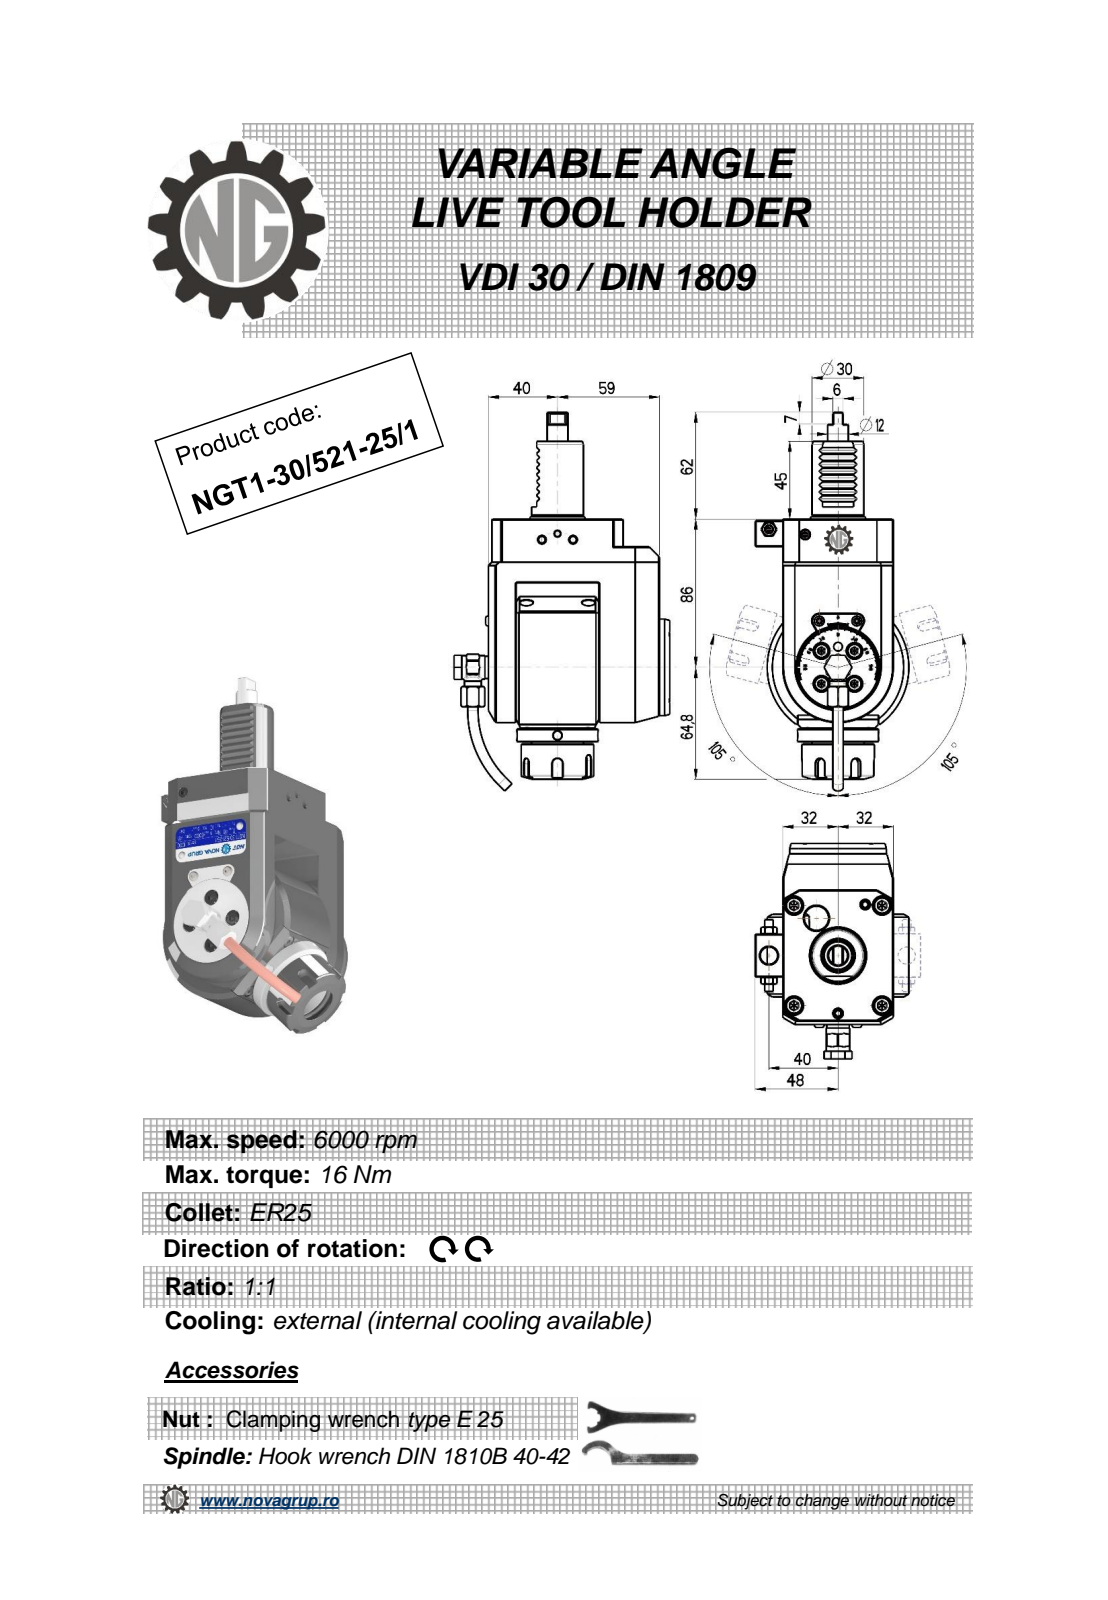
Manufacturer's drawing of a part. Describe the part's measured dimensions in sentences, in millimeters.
The part is named "NGT1_30_521_25_1". Its 3-D file was written by "PRO/ENGINEER BY PARAMETRIC TECHNOLOGY CORPORATION, 2010280 (CONFIG_CONTROL_DESIGN)". It is 1 solid with 544 faces: 229 planar, 132 cylindrical and 183 other. Overall it measures 219.67 by 124.9 by 89 millimeters. Its volume is 779 434 cubic millimeters and its surface area 74 506 square millimeters. Round holes: 3 of diameter 4, 2 of diameter 5, 2 of diameter 10, 1 of diameter 3, 1 of diameter 4.2, 1 of diameter 6.2, 1 of diameter 9, 1 of diameter 9.5, 1 of diameter 11, 1 of diameter 20.3. Round bosses or shafts: 2 of diameter 6, 2 of diameter 5.7, 1 of diameter 82, 1 of diameter 56, 1 of diameter 47, 1 of diameter 42, 1 of diameter 35, 1 of diameter 30. Partial cylindrical surfaces (rounded edges, fillets, slot ends): 12 of radius 0.26, 8 of radius 0.3, 6 of radius 0.16, 6 of radius 0.5, 5 of radius 3, 2 of radius 1, 1 of radius 7.7, 1 of radius 32. The main face-to-face distances are 64, 16, 37, 6, 99, 105, 21, 35, 14, 41. The hole center spacings are 0.4, 39.45, 40, 49, 49.4, 63.25, 63.56, 89.44.
